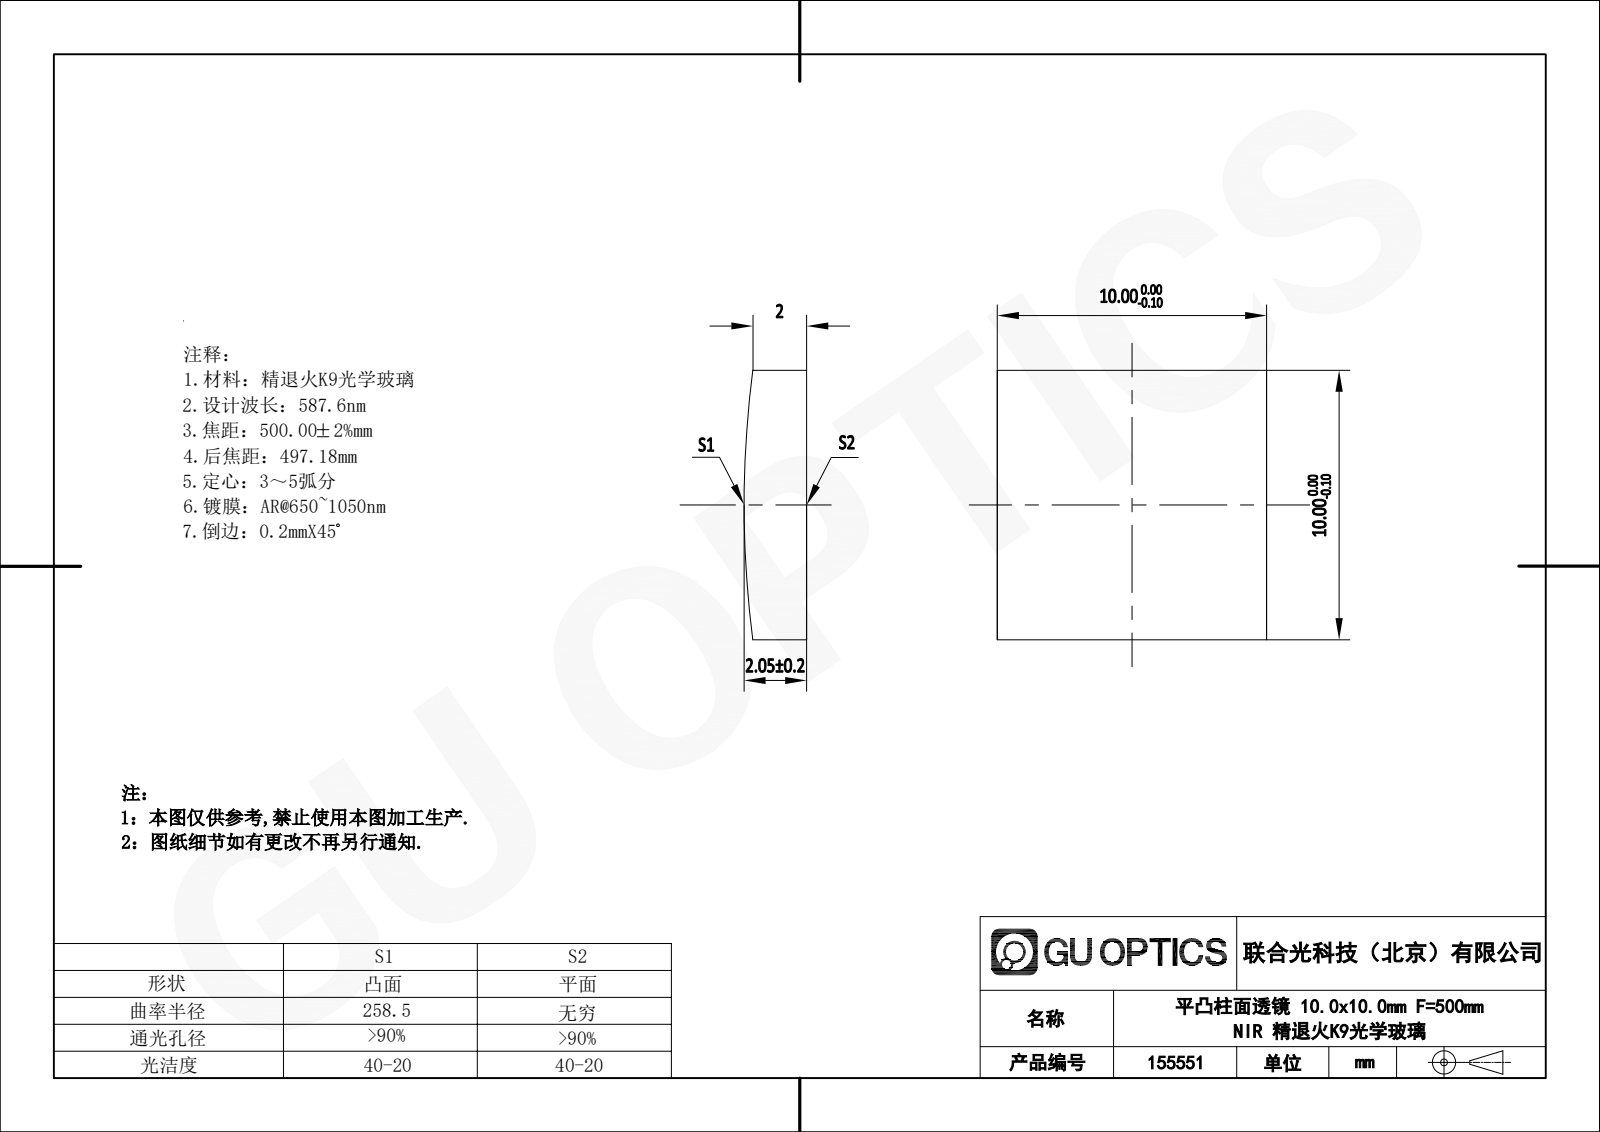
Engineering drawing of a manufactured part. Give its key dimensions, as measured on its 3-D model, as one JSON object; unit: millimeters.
{"part_name": "155527", "step_written_by": "SolidWorks 2020 (CONFIG_CONTROL_DESIGN)", "units": "millimeters", "bodies": {"solids": 1, "faces": 7, "planar": 5, "cylindrical": 2, "other": 0}, "overall_size": [10, 10, 2.05], "volume_mm3": 203, "surface_area_mm2": 281, "partial_cylinders_radius": [[258.5, 1]], "face_to_face_distances": [10]}
